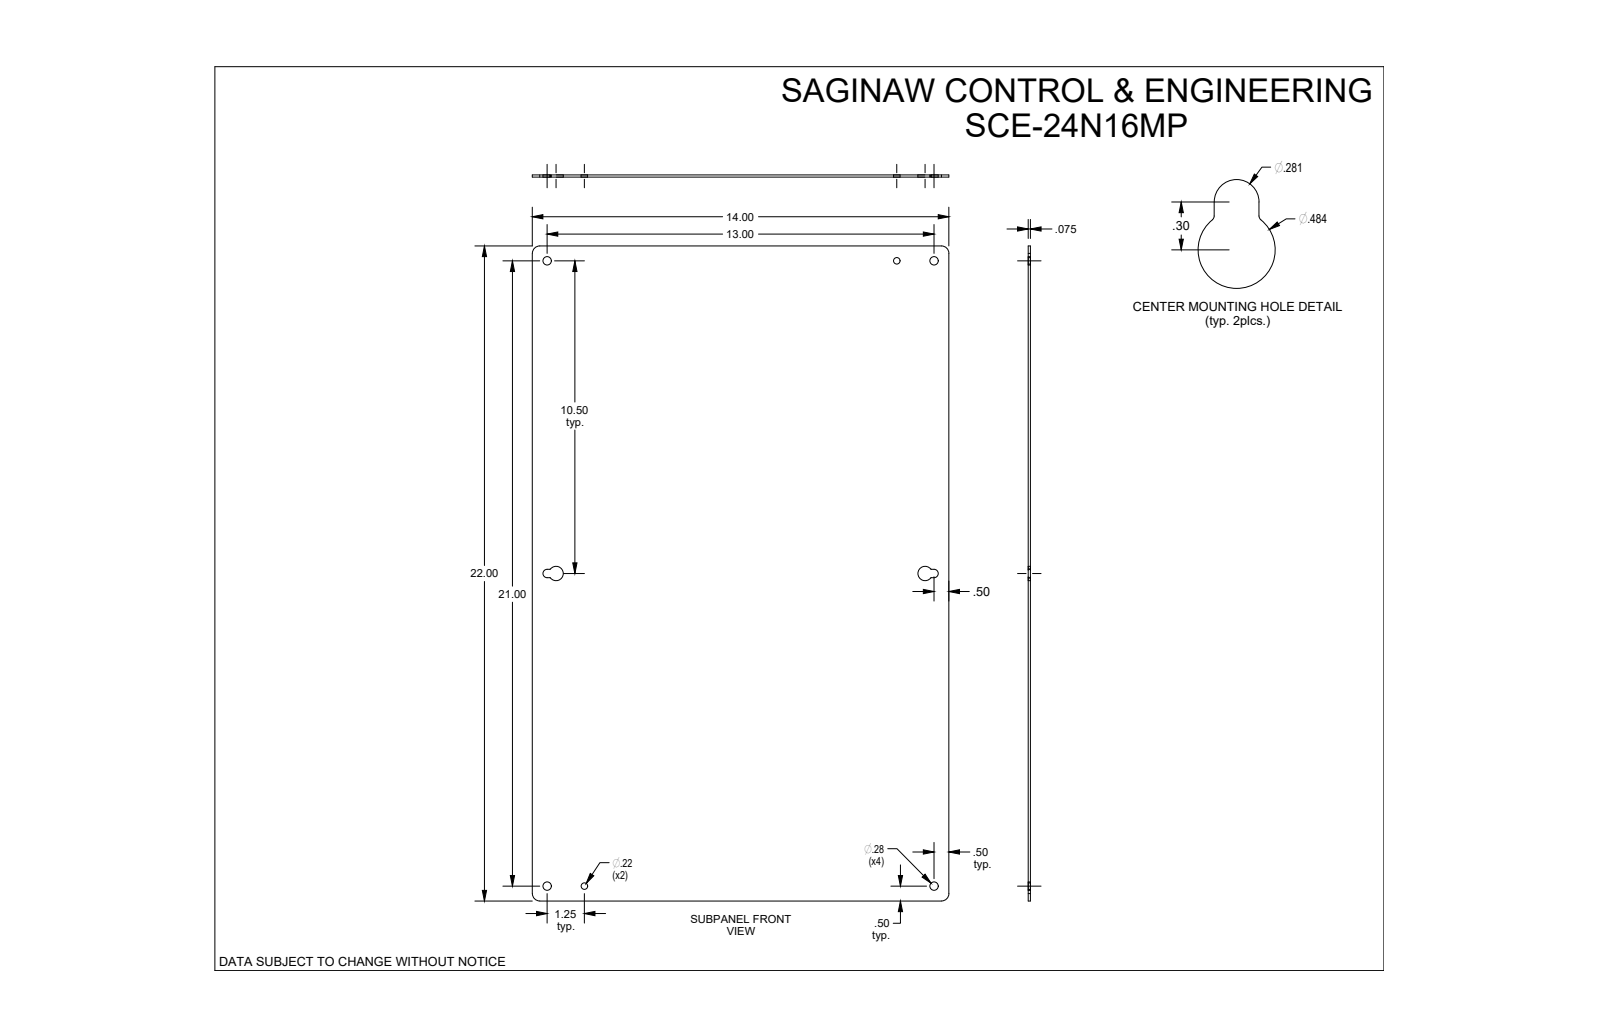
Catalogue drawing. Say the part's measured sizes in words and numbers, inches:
The part is named "SCE-24N16MP". Its 3-D file was written by "SolidWorks 2019 (CONFIG_CONTROL_DESIGN)". It is 1 solid with 28 faces: 10 planar, 18 cylindrical and 0 other. Overall it measures 22 by 14 by 0.075 inches. Its volume is 23.04 cubic inches and its surface area 620.3 square inches. Round holes: 4 of diameter 0.281, 2 of diameter 0.218. Partial cylindrical surfaces (rounded edges, fillets, slot ends): 4 of radius 0.03, 4 of radius 0.25, 2 of radius 0.141, 2 of radius 0.242. The main face-to-face distances are 0.075, 14, 22, 10.859, 11.141, 0.281. The hole center spacings are 1.25, 11.75, 13, 21, 21.037, 24.064, 24.698, 23.479.
